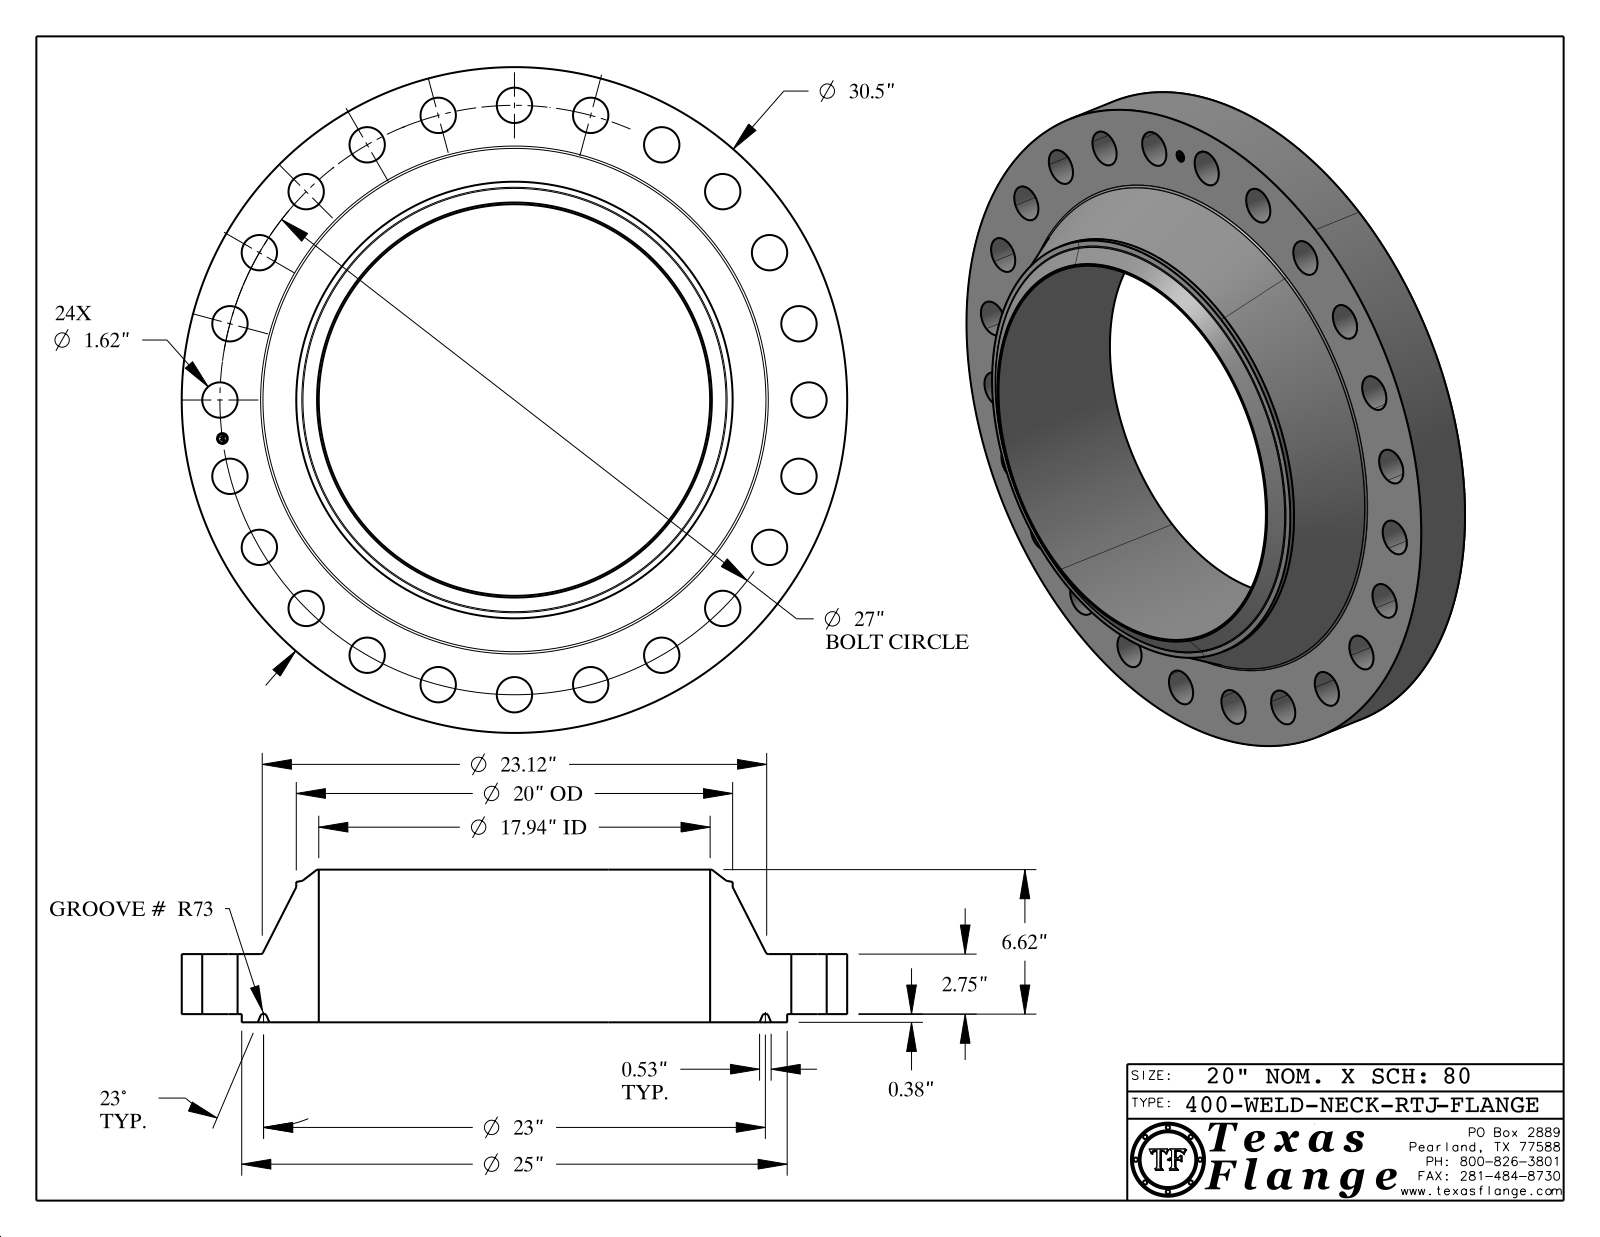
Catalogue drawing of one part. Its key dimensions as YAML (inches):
part_name: "400-WELD-NECK-RTJ"
step_written_by: "CATIA V5 STEP AP214 (AUTOMOTIVE_DESIGN)"
units: inches
bodies: {solids: 1, faces: 465, planar: 371, cylindrical: 76, other: 18}
overall_size: [30.5, 30.5, 6.995]
volume: 1634
surface_area: 2066
round_holes:
  - {diameter: 1.62, count: 24}
  - {diameter: 0.495, count: 1}
  - {diameter: 17.938, count: 1}
round_bosses_or_shafts:
  - {diameter: 0.03, count: 8}
  - {diameter: 30.5, count: 1}
  - {diameter: 25, count: 1}
  - {diameter: 20, count: 1}
  - {diameter: 0.39, count: 1}
face_to_face_distances: [3.125, 0.375, 2.75, 6.995, 6.62, 3.87, 3.11, 2.735, 0.015, 3.885]
hole_center_spacings: [13.5, 3.524, 6.988, 10.333, 16.437, 24.945, 26.769, 21.421]
